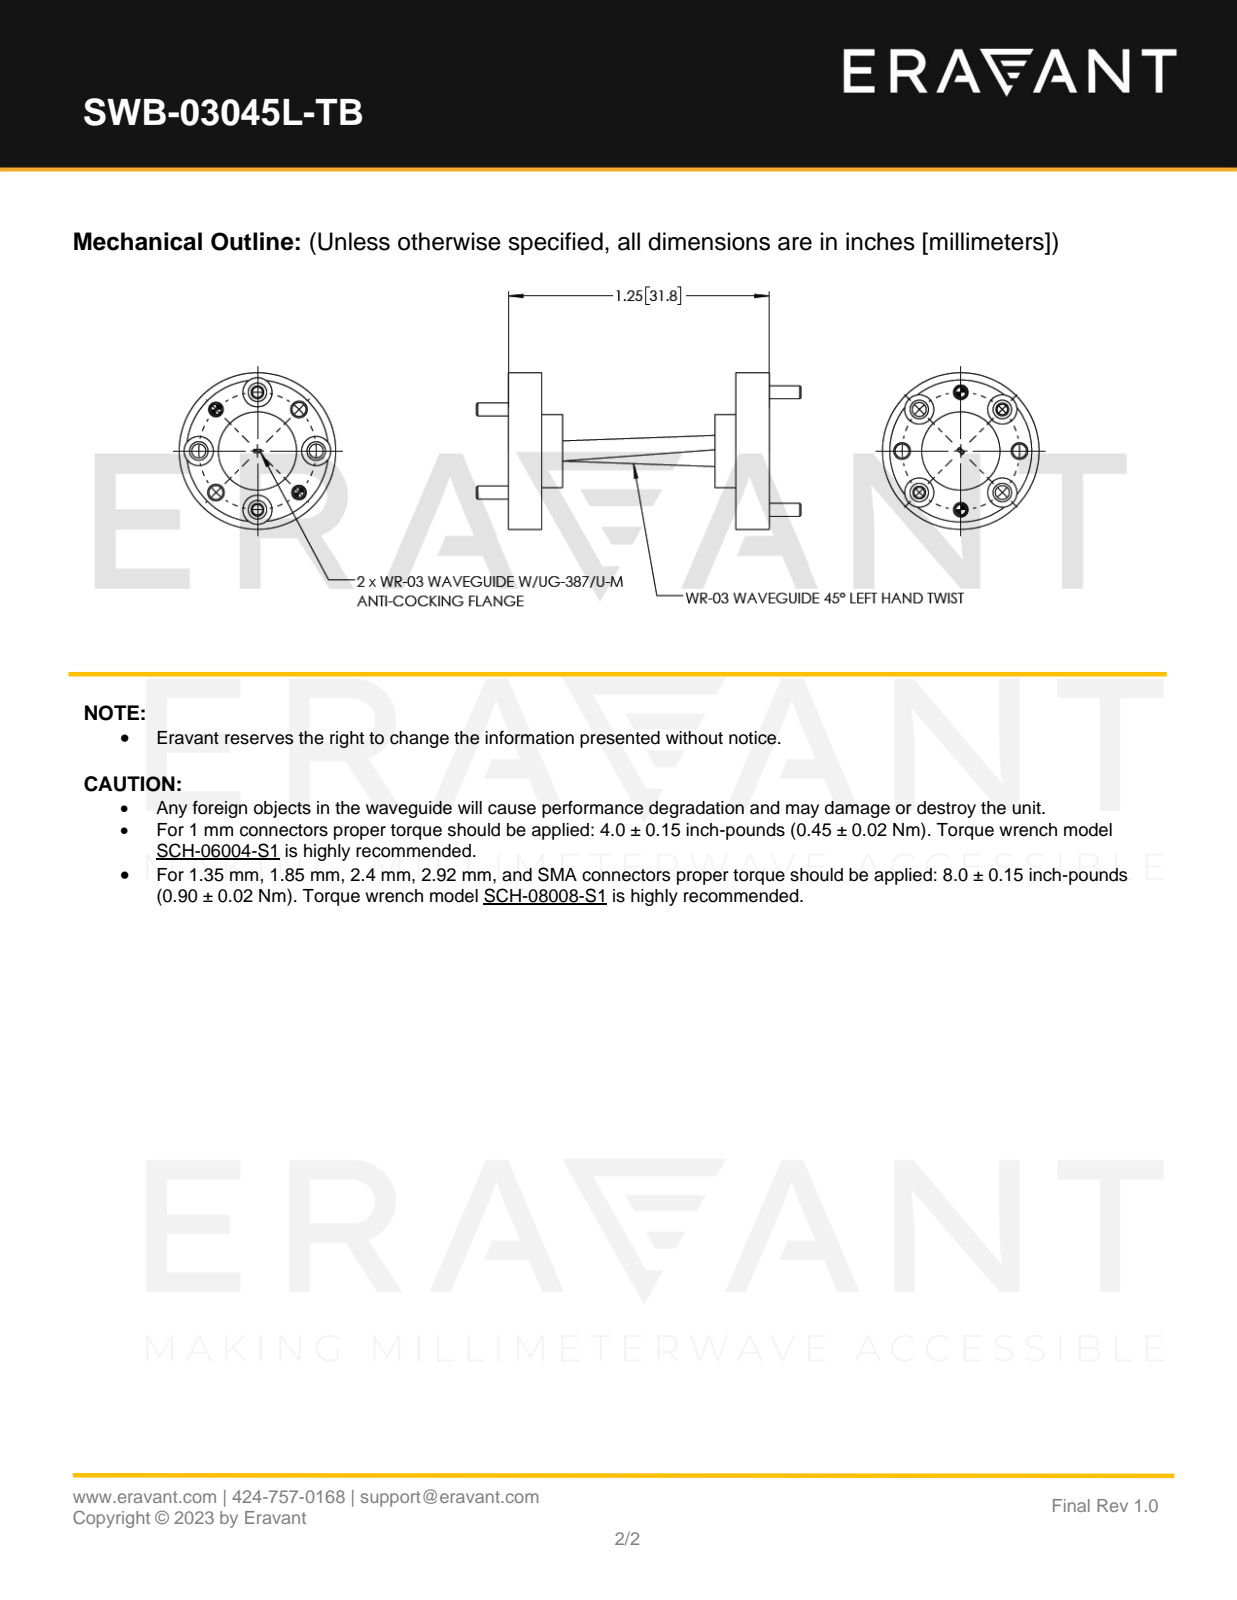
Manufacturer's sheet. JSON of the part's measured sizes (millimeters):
{"part_name": "WB-T03-5-A, Rev 1.0, CTRLD", "step_written_by": "SolidWorks 2021 (AUTOMOTIVE_DESIGN)", "units": "millimeters", "bodies": {"solids": 5, "faces": 157, "planar": 36, "cylindrical": 77, "other": 44}, "overall_size": [39.5, 19.1, 19.1], "volume_mm3": 2380, "surface_area_mm2": 2451, "round_holes": [[2.3, 8], [3.6, 8], [1.5, 4], [1.7, 4], [17.3, 1]], "round_bosses_or_shafts": [[1.6, 4], [19.1, 1], [9.5, 1], [9.5, 1], [7.9, 1]], "face_to_face_distances": [0.5, 31.2, 23.6, 27.2, 3.6, 3.6, 27.2, 30.7, 4.1, 27.7], "hole_center_spacings": [13.2, 5.5, 10.1, 5.5, 10.1, 7.1, 14.3, 7.1]}
